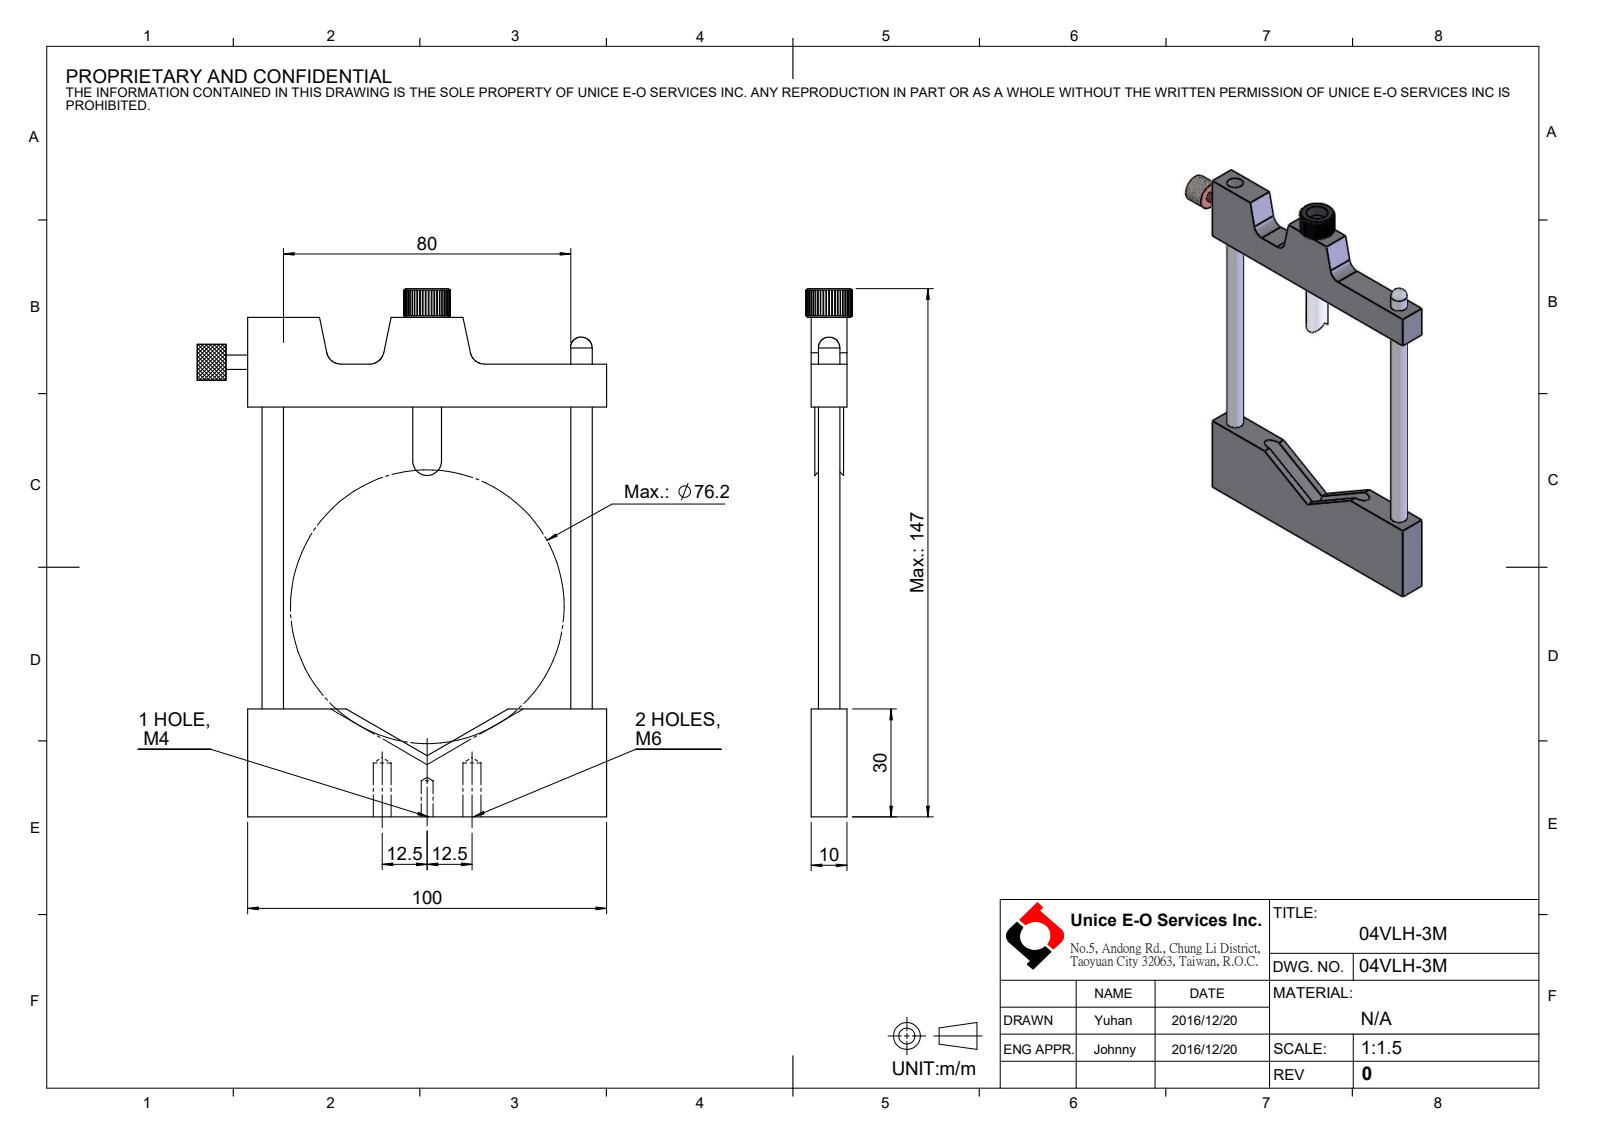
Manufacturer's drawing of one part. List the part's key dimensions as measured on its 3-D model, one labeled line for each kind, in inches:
Part name (STEP PRODUCT): 04VLH-3M
STEP written by: SolidWorks 2016 (CONFIG_CONTROL_DESIGN)
Units: inches
Bodies: 8 solids, 215 faces (37 planar, 154 cylindrical, 24 other)
Overall size (bounding box): 5.787 × 4.488 × 0.511
Volume: 3.04 in³ · Surface area: 38.13 in²
Round holes (diameter × count): ⌀0.13 ×2, ⌀0.197 ×2, ⌀0.236 ×2, ⌀0.165 ×1, ⌀0.315 ×1, ⌀0.335 ×1
Round bosses / shafts (diameter × count): ⌀0.394 ×1, ⌀0.157 ×1
Partial cylindrical surfaces — rounded edges, fillets, slot ends (radius × count): R0.016 ×50, R0.157 ×3, R0.256 ×1
Main face-to-face distances: 0.394, 4.488, 5.472, 0.984, 1.181, 3.307, 4.291, 0.512, 3.937, 3.78
Hole centre spacings: 0.492, 1.201, 1.693, 2.185, 0.984, 3.386
